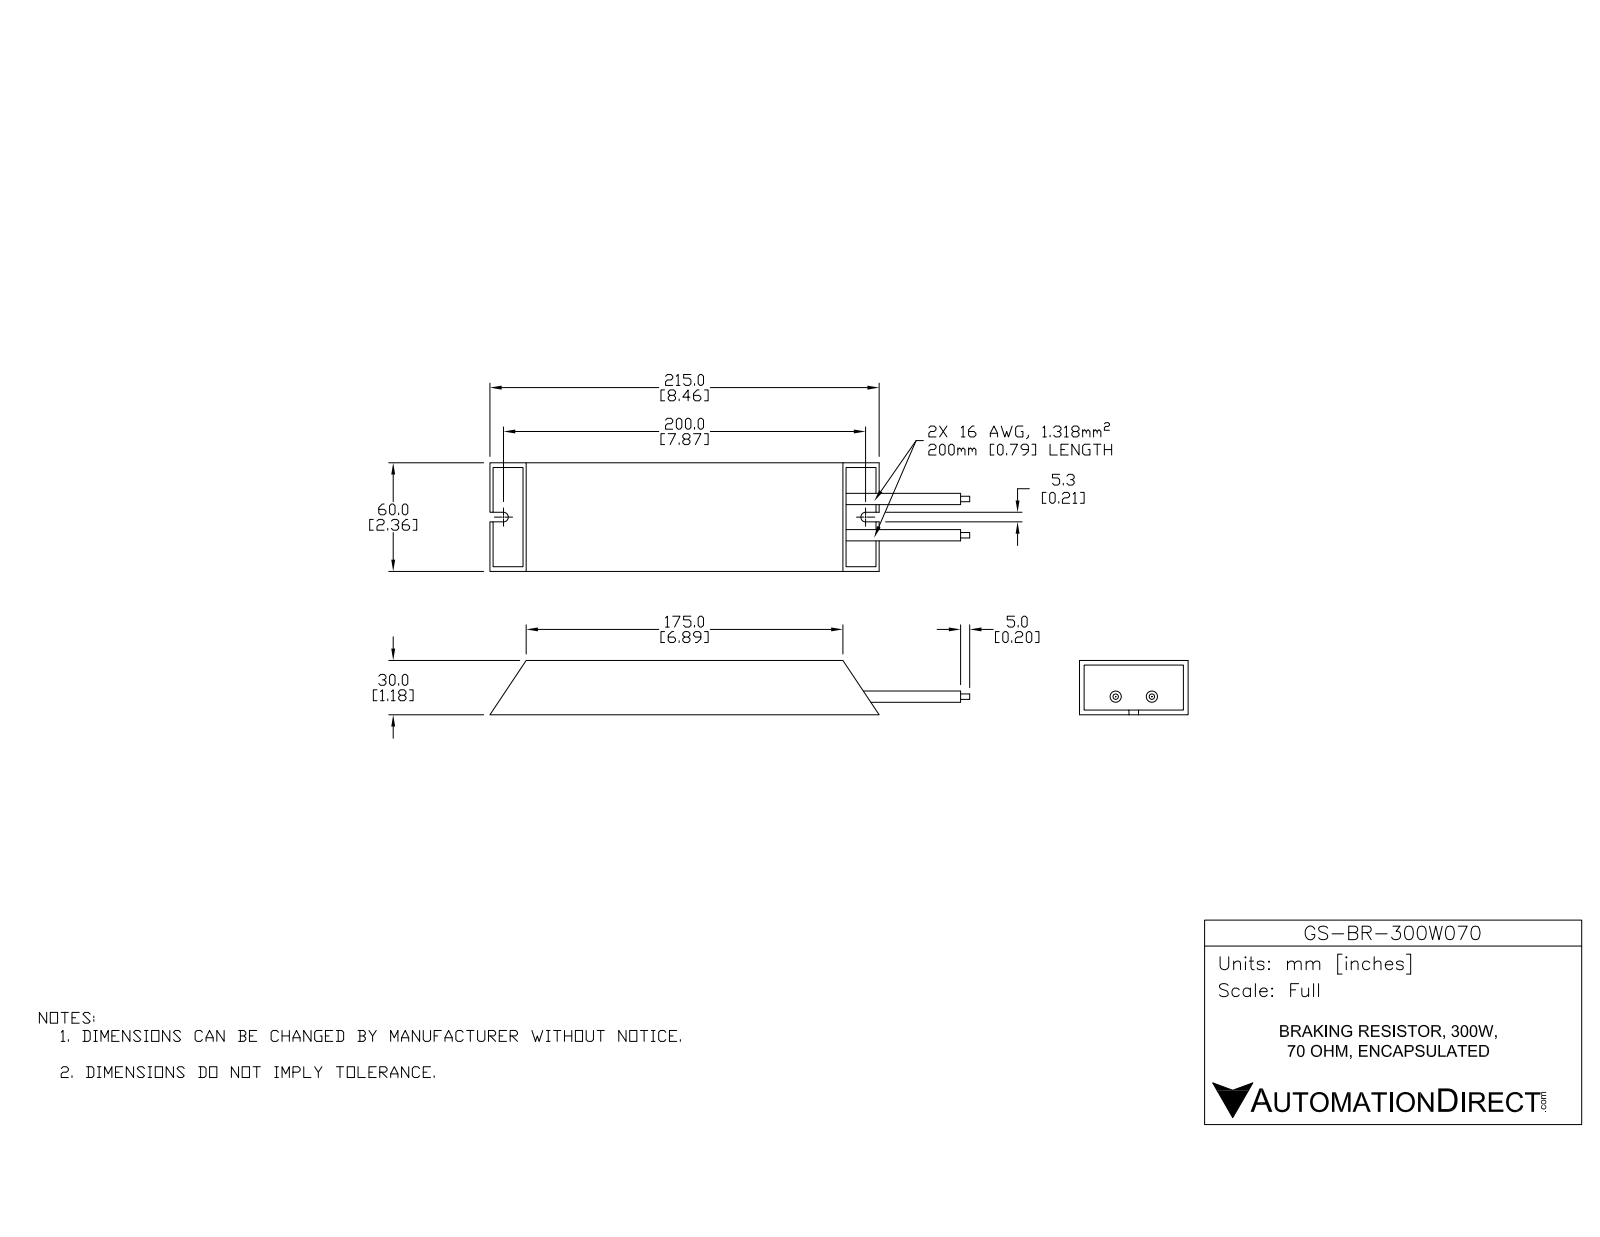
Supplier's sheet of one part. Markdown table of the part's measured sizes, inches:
| quantity | value |
| --- | --- |
| part name | GS-BR-300W070 |
| STEP written by | SolidWorks 2015 (AUTOMOTIVE_DESIGN) |
| units | inches |
| bodies | 1 solid, 34 faces (24 planar, 10 cylindrical, 0 other) |
| overall size | 10.433 × 2.362 × 1.181 |
| volume | 19.99 in³ |
| surface area | 69.1 in² |
| round bosses / shafts (diameter × count) | 0.244 × 2, 0.118 × 2 |
| partial cylindrical surfaces (radius × count) | 0.104 × 2 |
| main face-to-face distances | 1.181, 2.362, 0.102, 1.079, 6.89, 2.26, 2.157, 0.976, 1.077, 1.285 |
